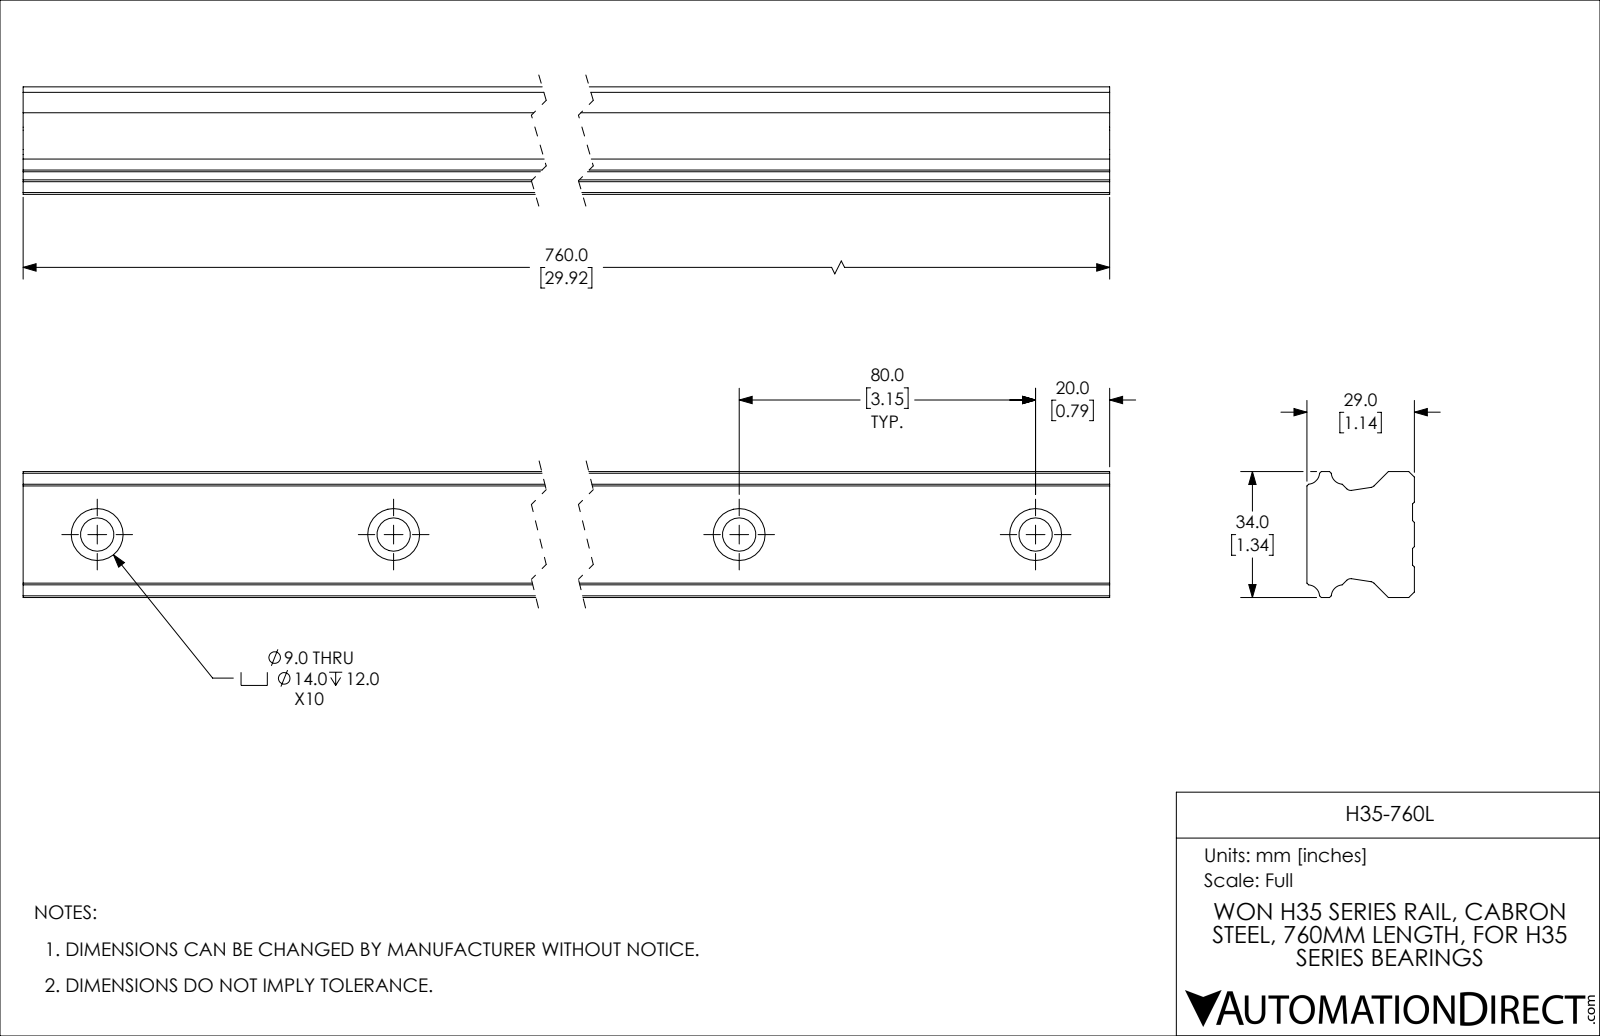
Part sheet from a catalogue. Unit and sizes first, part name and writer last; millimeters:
Units: millimetres
Overall size (bounding box): 760 × 34 × 29
Round holes (diameter × count): ⌀9 ×10, ⌀14 ×10
Partial cylindrical surfaces — rounded edges, fillets, slot ends (radius × count): R1.5 ×4, R3.2 ×4
Main face-to-face distances: 29, 0.5, 28.5, 34, 12.8, 15.13, 27.93, 40.72, 25.59, 12.79
Hole centre spacings: 80, 160, 240, 320, 400, 480, 560, 640
Volume: 616 132 mm³ · Surface area: 108 946 mm²
Bodies: 1 solid, 118 faces (70 planar, 48 cylindrical, 0 other)
Part name (STEP PRODUCT): H35-760L
STEP written by: SolidWorks 2019 (CONFIG_CONTROL_DESIGN)
